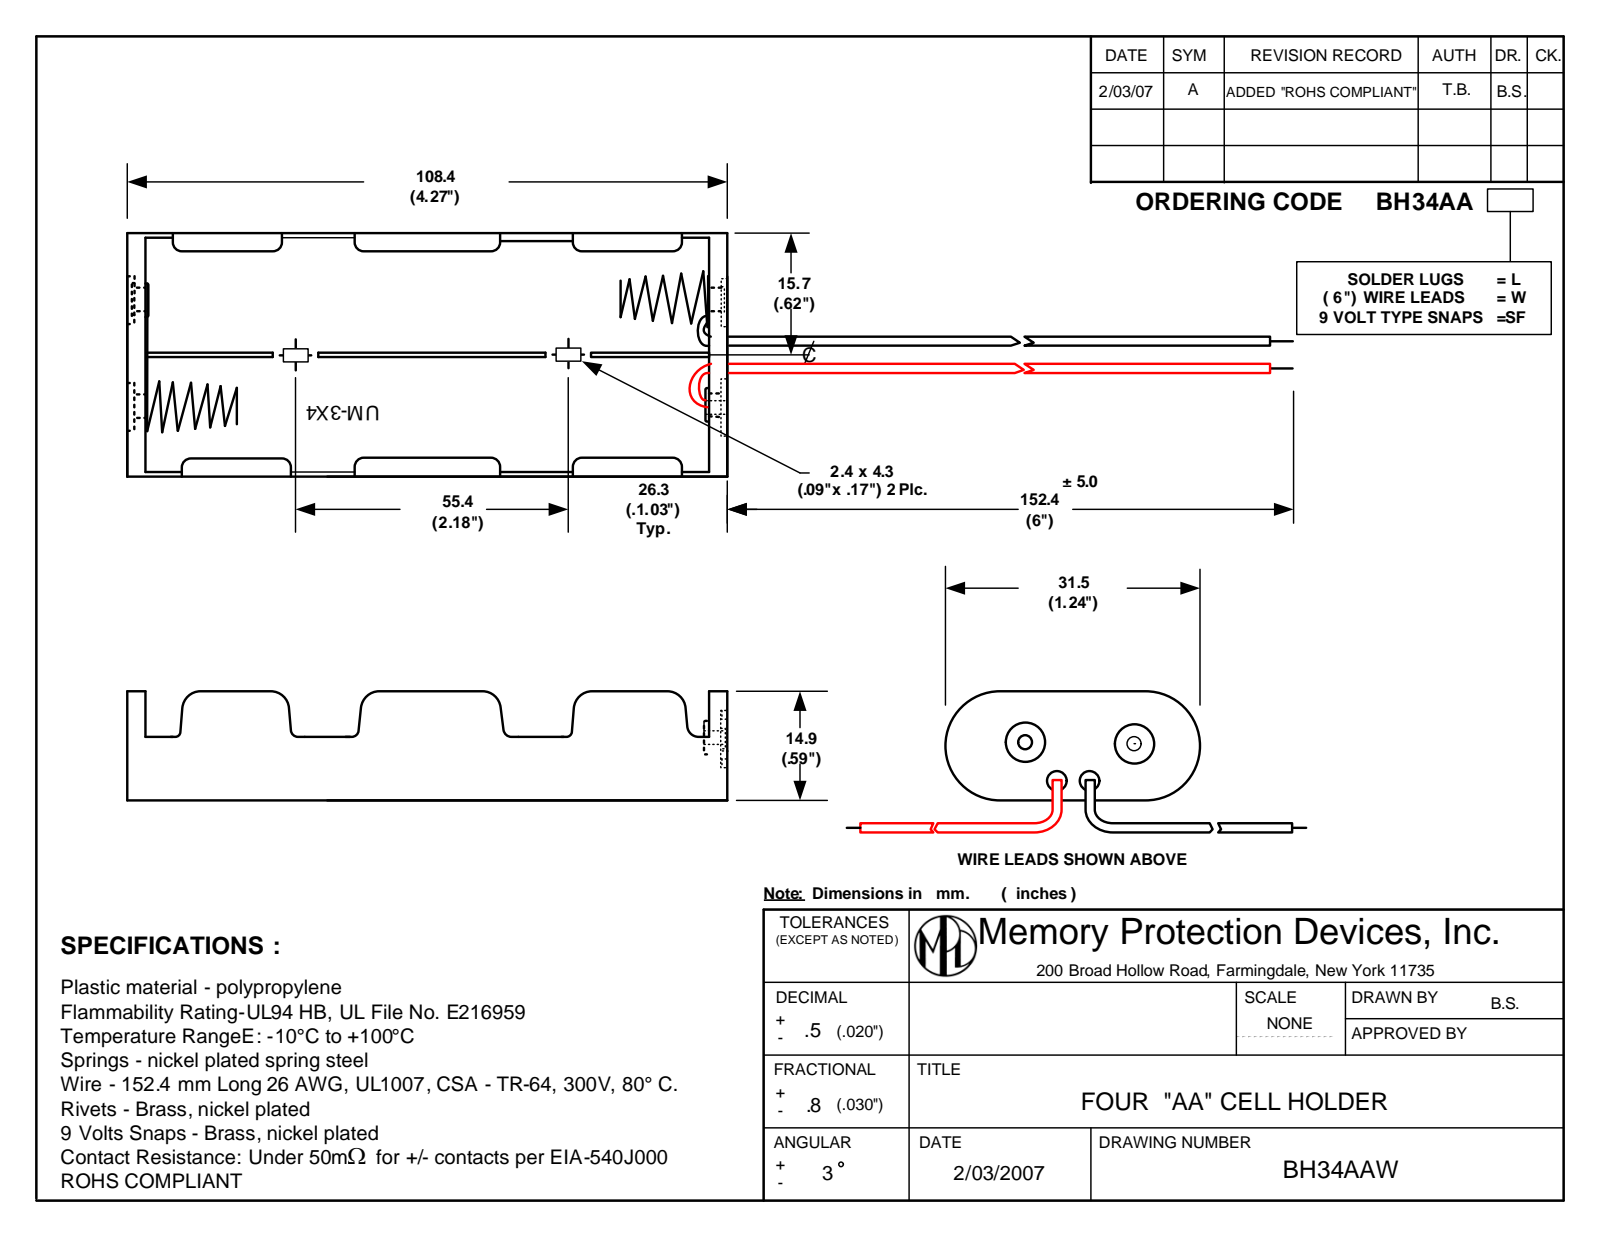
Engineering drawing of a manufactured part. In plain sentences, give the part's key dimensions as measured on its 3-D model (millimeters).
The part is named "BH34AAW". Its 3-D file was written by "SolidWorks 2017 (AUTOMOTIVE_DESIGN)". It is 9 solids with 288 faces: 133 planar, 107 cylindrical and 48 other. Overall it measures 258.4 by 31.5 by 14.9 millimeters. Its volume is 8 259 cubic millimeters and its surface area 16 482 square millimeters. Round holes: 2 of diameter 0.48, 2 of diameter 1.4, 2 of diameter 2.2, 2 of diameter 7.5. Round bosses or shafts: 2 of diameter 3.5, 2 of diameter 3.4, 2 of diameter 1.3, 2 of diameter 0.7. Partial cylindrical surfaces (rounded edges, fillets, slot ends): 18 of radius 1, 4 of radius 5.8, 4 of radius 7. The main face-to-face distances are 1.2, 1, 107.2, 106, 108.4, 30.3, 0.31, 108.09, 0.89, 106.89. The hole center spacings are 2.6, 8.22, 8.29, 10.31, 10.39, 15.
